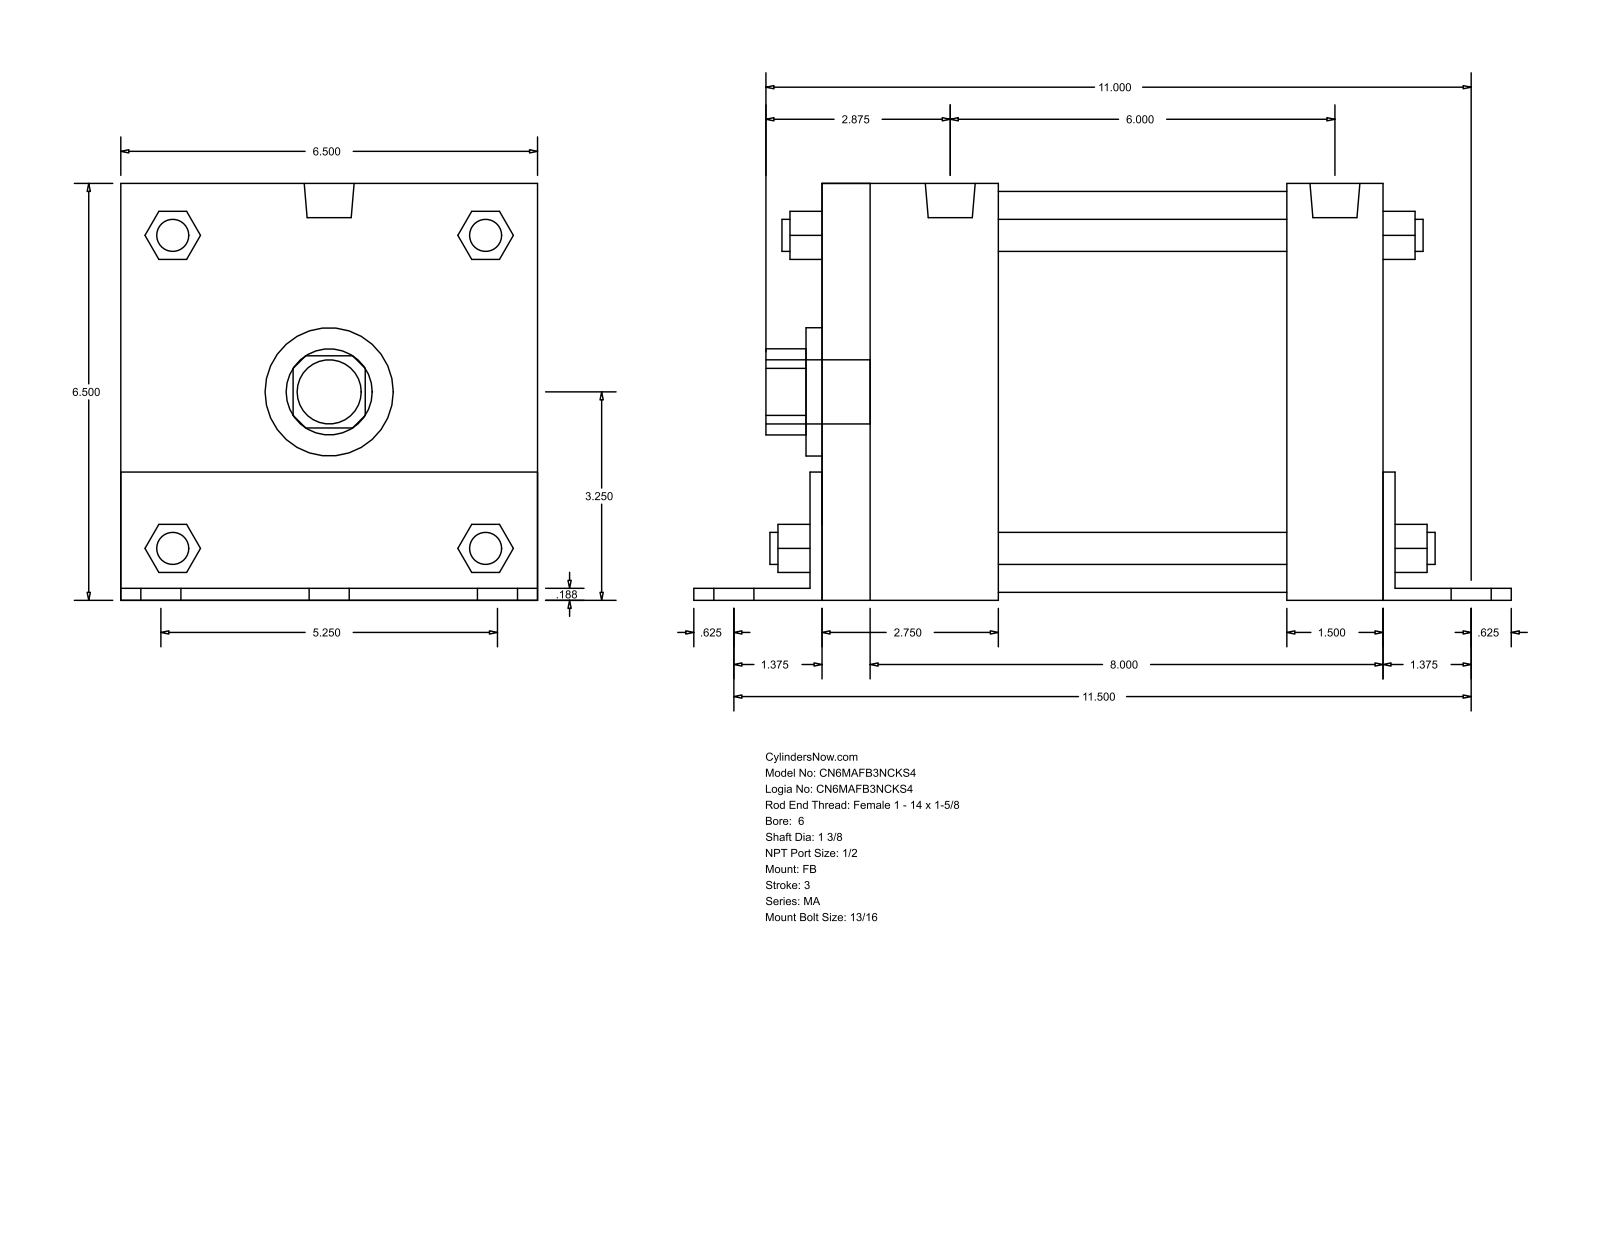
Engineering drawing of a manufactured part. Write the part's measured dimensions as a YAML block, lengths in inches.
part_name: "MA_FB__0600_1.375"
step_written_by: "GSSL Pune (CONFIG_CONTROL_DESIGN)"
units: inches
bodies: {solids: 0, faces: 140, planar: 105, cylindrical: 35, other: 0}
overall_size: [12.625, 6.502, 6.5]
round_holes:
  - {diameter: 1.375, count: 1}
  - {diameter: 2, count: 1}
  - {diameter: 6.25, count: 1}
round_bosses_or_shafts:
  - {diameter: 0.813, count: 6}
  - {diameter: 0.687, count: 4}
  - {diameter: 0.5, count: 4}
  - {diameter: 0.778, count: 2}
  - {diameter: 1, count: 1}
partial_cylinders:
  - {radius: 0.672, count: 1}
  - {radius: 1.262, count: 1}
face_to_face_distances: [6.5, 0.187, 8.625, 6.502, 0.185, 6.315, 0.188, 1.5, 8.813, 9]
